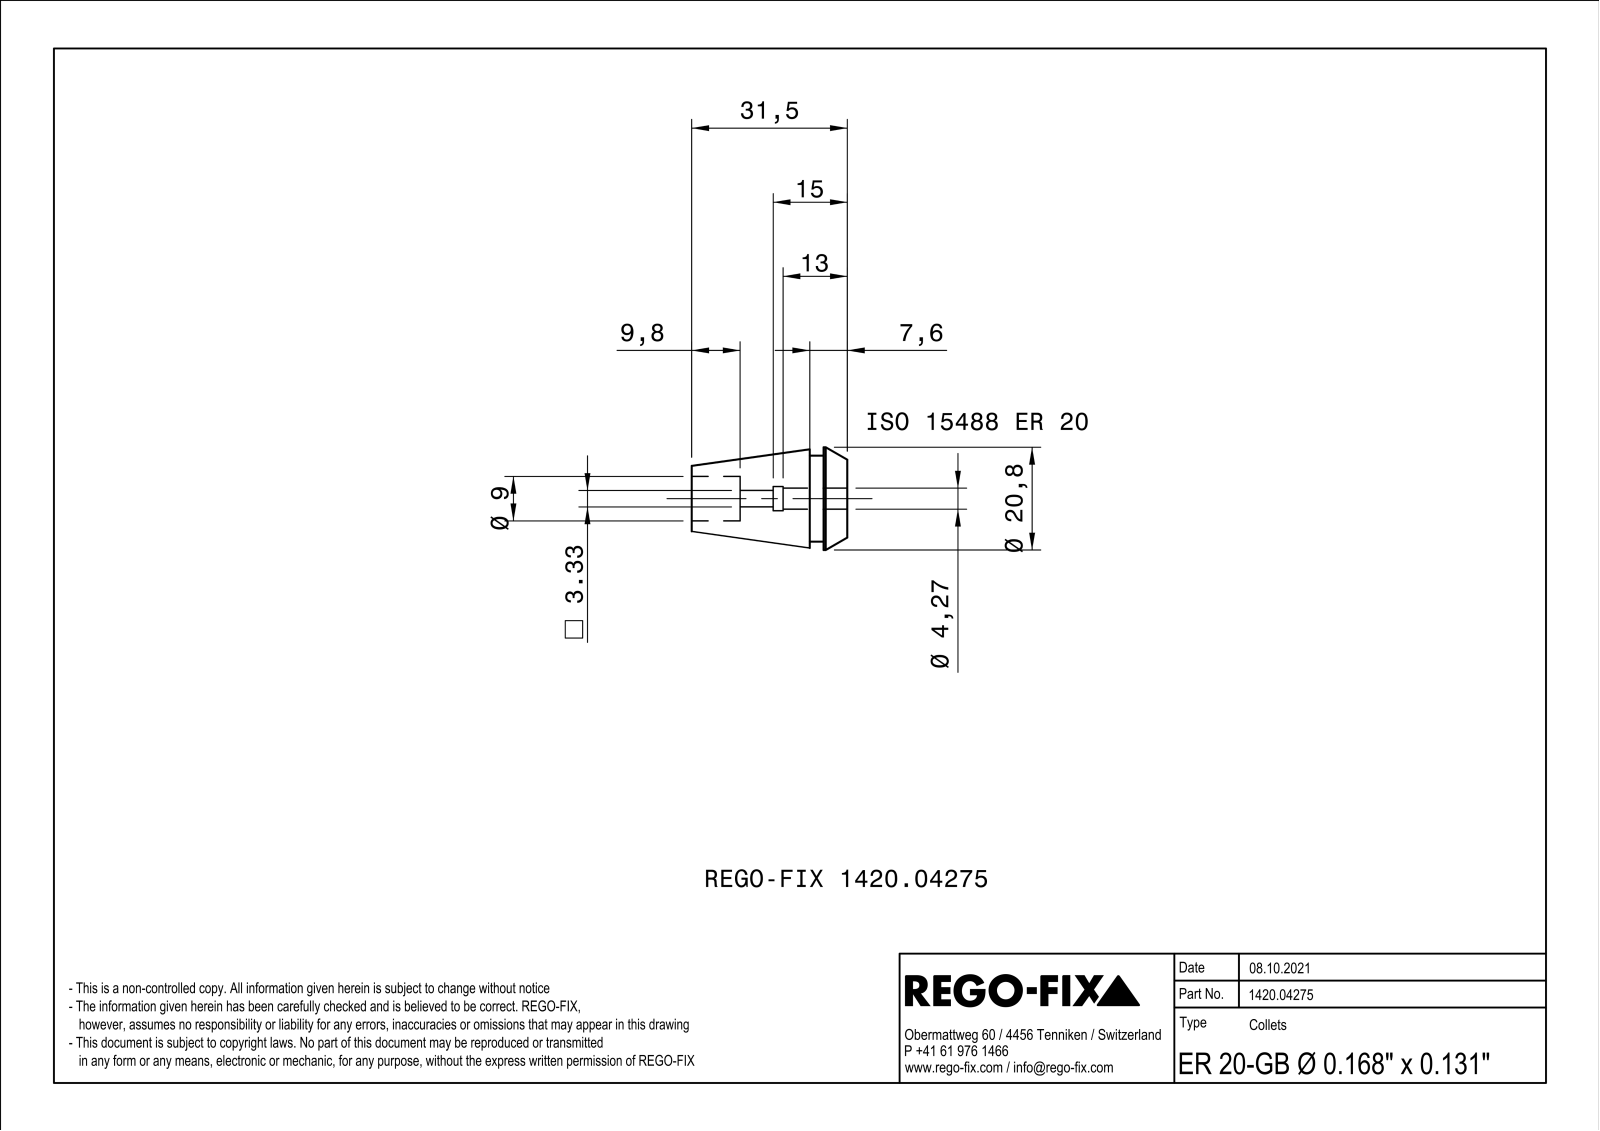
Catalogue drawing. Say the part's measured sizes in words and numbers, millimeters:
The part is named "NOCUT". Its 3-D file was written by "SIEMENS PLM Software Solid Edge ST10 (AUTOMOTIVE_DESIGN)". It is 1 solid with 152 faces: 60 planar, 28 cylindrical and 64 other. Overall it measures 31.5 by 20.79 by 20.79 millimeters. Its volume is 5 293 cubic millimeters and its surface area 4 867 square millimeters. Round holes: 1 of diameter 9. Round bosses or shafts: 1 of diameter 17.4. Partial cylindrical surfaces (rounded edges, fillets, slot ends): 1 of radius 1.9, 1 of radius 2.13, 1 of radius 2.45. The main face-to-face distances are 0.8, 4.8, 31.5, 26.7, 21.7, 16.9, 9.8, 1.4, 2.2, 7.6.
